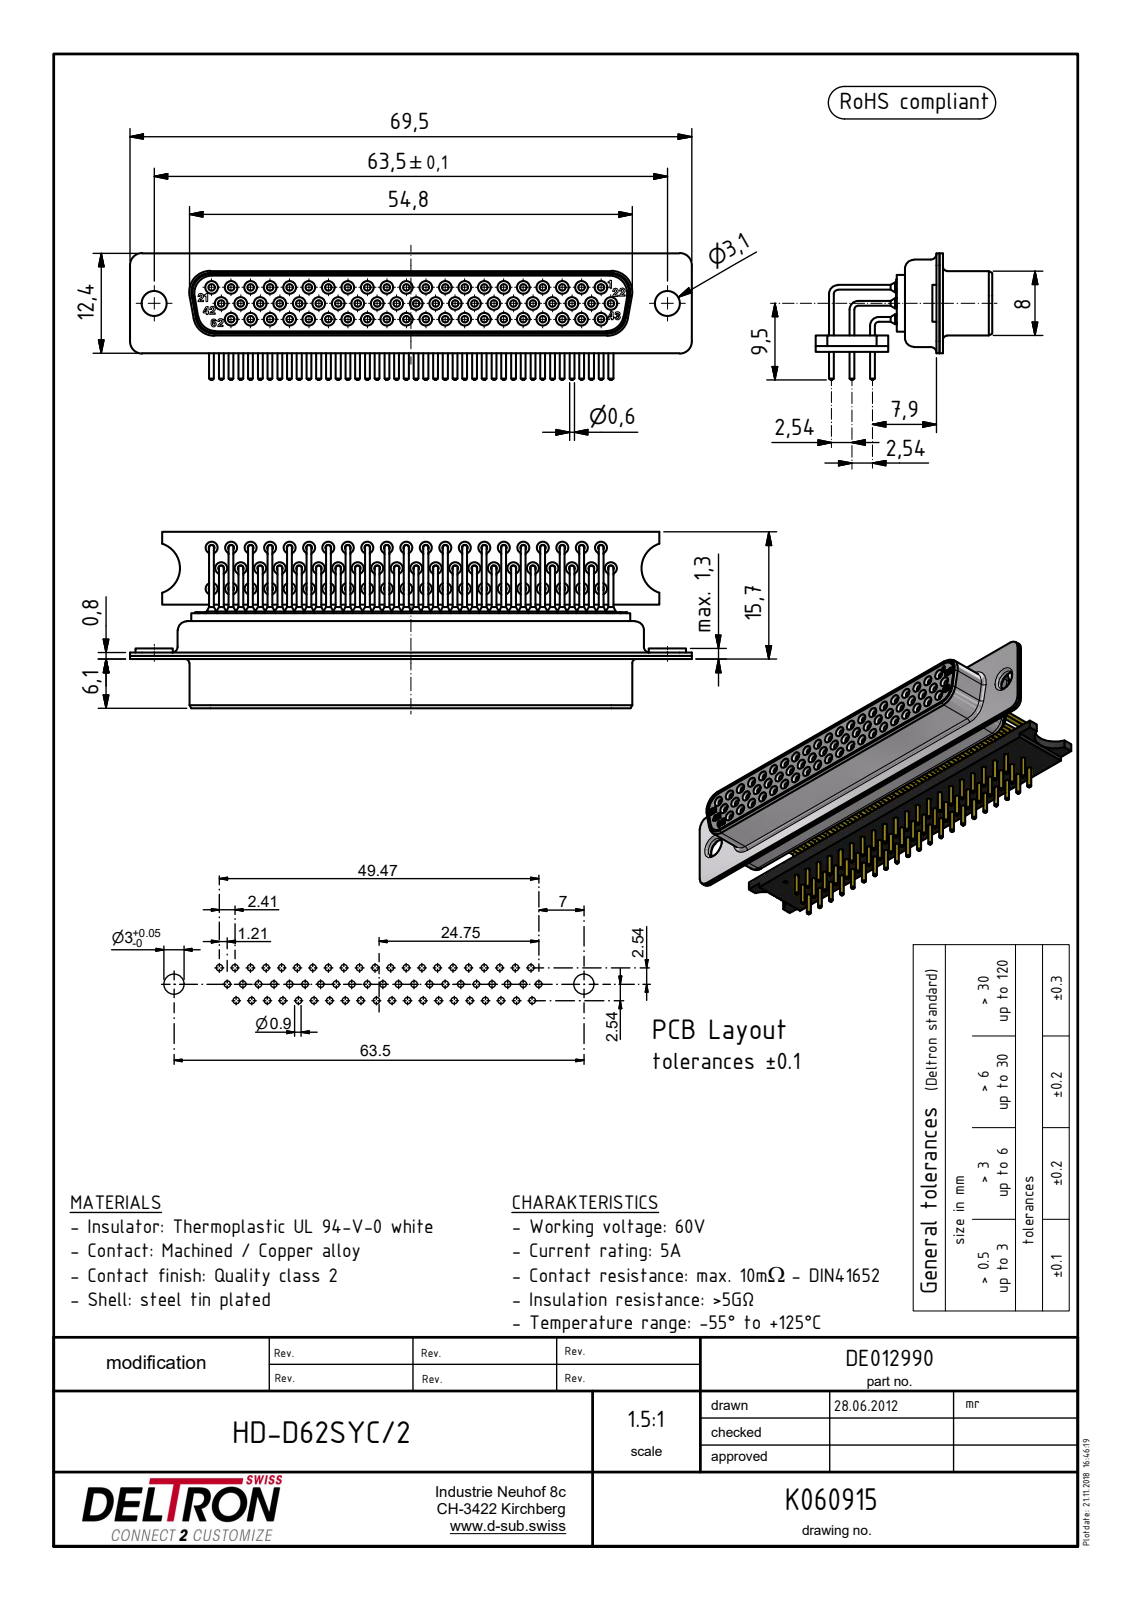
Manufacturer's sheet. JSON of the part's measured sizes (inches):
{"part_name": "N00679_China_BG; R+B00747_BG; R+B00749_BG; R+B00748_BG (+4 more)", "step_written_by": "Autodesk Inventor 2015 (AUTOMOTIVE_DESIGN)", "units": "inches", "bodies": {"solids": 66, "faces": 2510, "planar": 1170, "cylindrical": 829, "other": 511}, "overall_size": [2.736, 0.86, 0.618], "volume_in3": 0.402, "surface_area_in2": 27.16, "round_holes": [[0.028, 63], [0.031, 62], [0.035, 62], [0.05, 62], [0.055, 62], [0.063, 62], [0.122, 2], [0.16, 2]], "round_bosses_or_shafts": [[0.024, 124], [0.05, 62], [0.049, 62], [0.181, 2], [0.154, 2]], "partial_cylinders_radius": [[0.028, 8], [0.043, 8], [0.059, 8], [0.079, 8], [0.087, 8], [0.051, 6], [0.01, 4], [0.02, 4]], "face_to_face_distances": [0.016, 0.055, 0.354, 0.293, 0.022, 0.079, 0.278, 0.299, 0.35, 0.335], "hole_center_spacings": [0.095, 0.19, 0.285, 0.38, 0.111, 0.474, 0.569, 0.664]}
